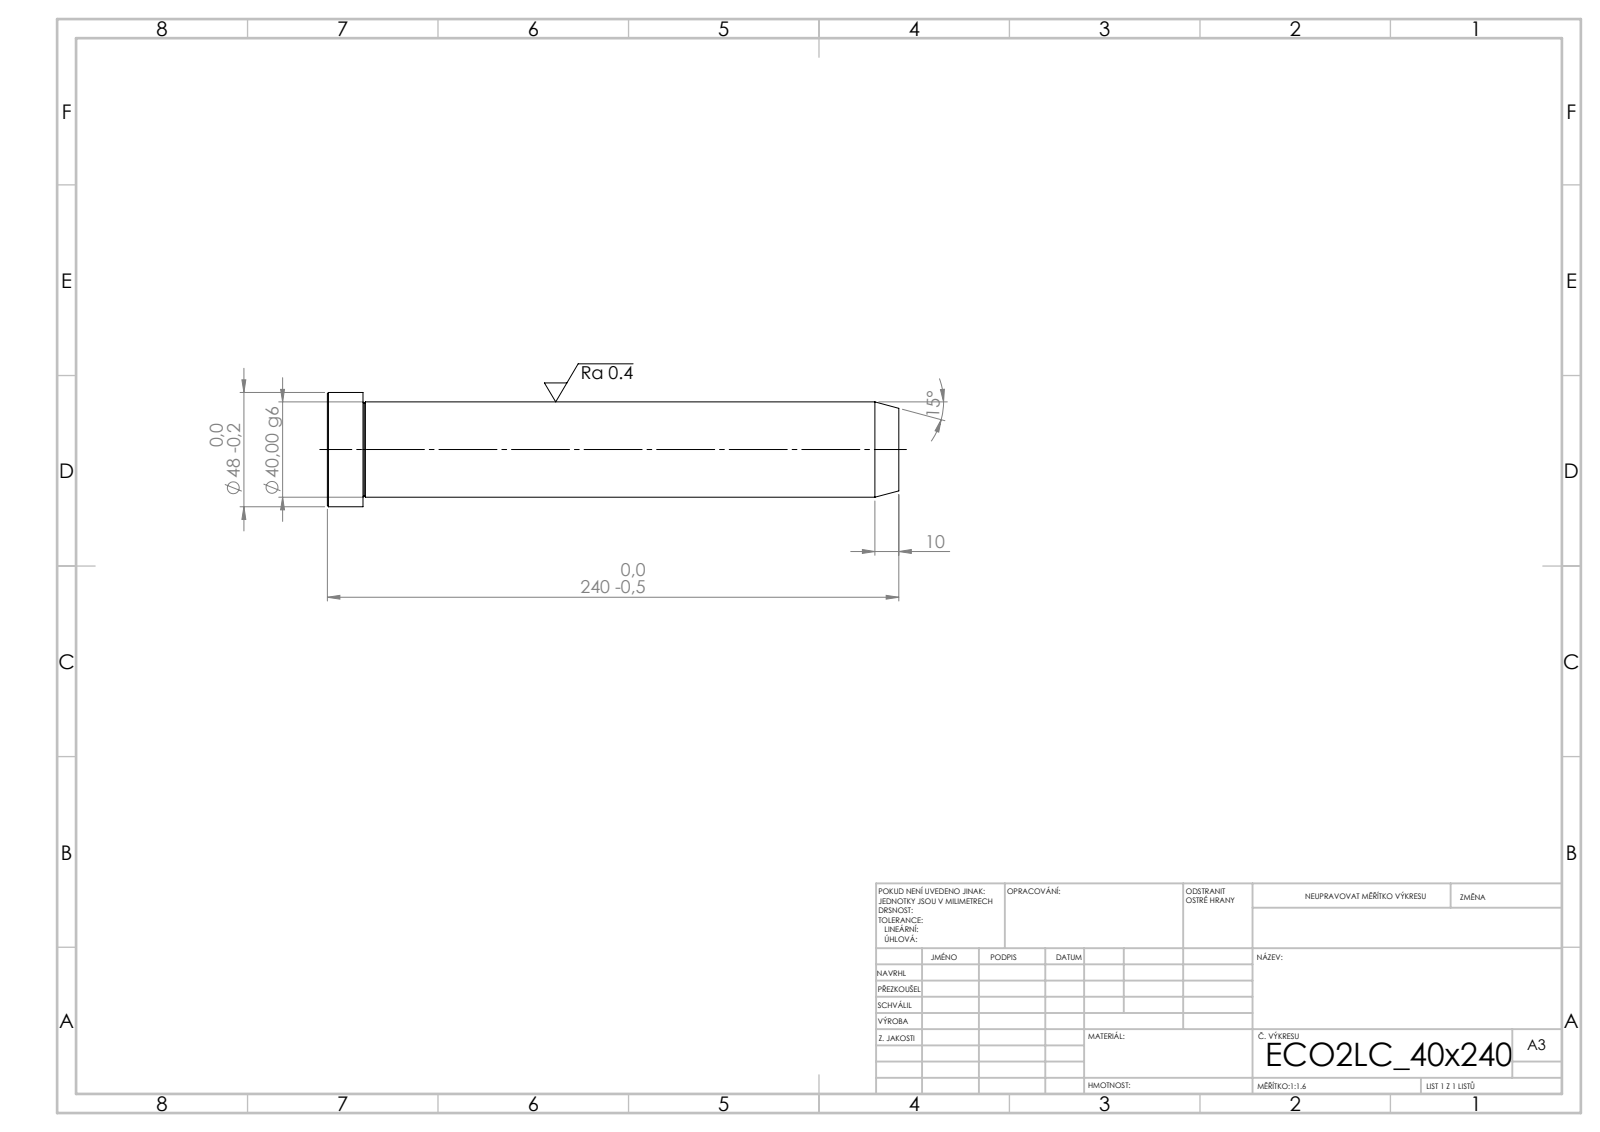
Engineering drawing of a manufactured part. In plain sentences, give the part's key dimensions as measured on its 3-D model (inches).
Its 3-D file was written by "SolidWorks 2019 (CONFIG_CONTROL_DESIGN)". It is 1 solid with 15 faces: 3 planar, 4 cylindrical and 8 other. Overall it measures 9.449 by 1.89 by 1.89 inches. Its volume is 18.81 cubic inches and its surface area 52.43 square inches. Round bosses or shafts: 1 of diameter 1.89, 1 of diameter 1.575. The main face-to-face distances are 9.449, 8.858, 0.591.
